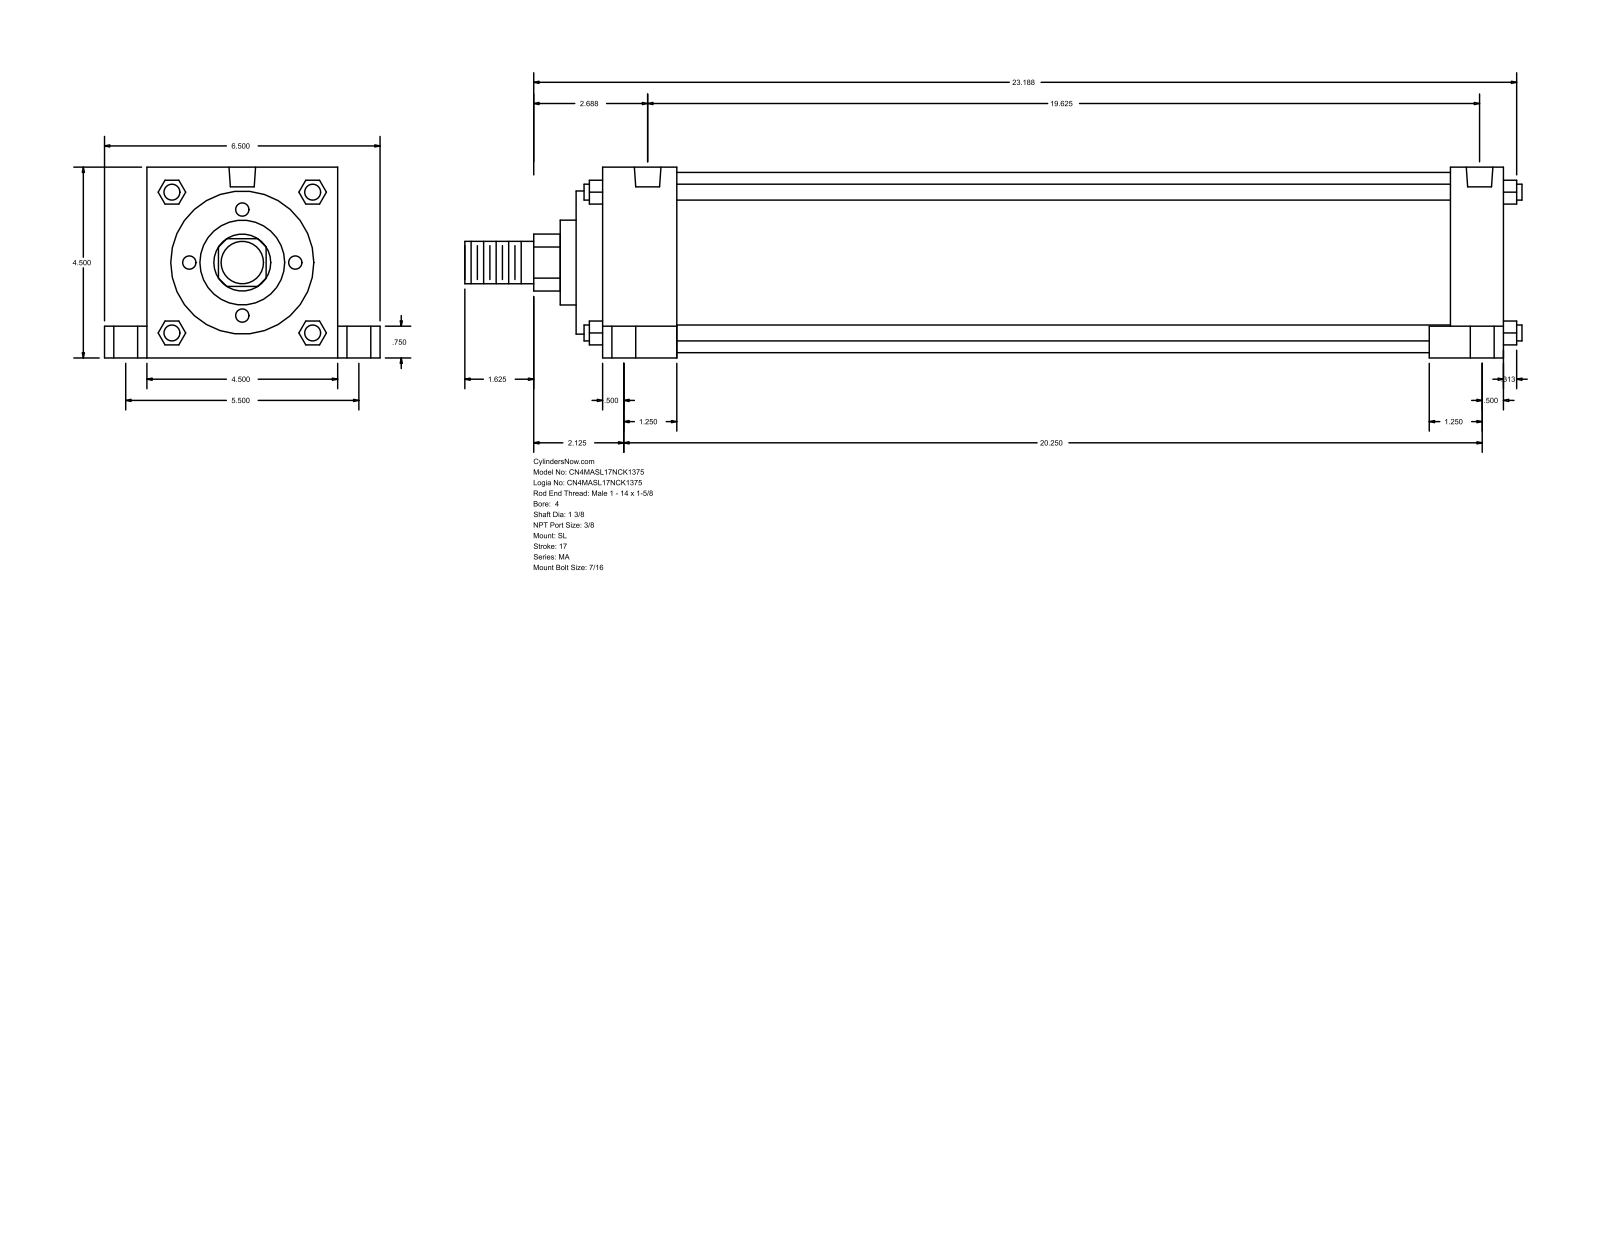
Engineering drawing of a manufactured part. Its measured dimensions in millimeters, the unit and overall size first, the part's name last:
Units: millimetres
Overall size (bounding box): 633.41 × 165.1 × 114.3
Round holes (diameter × count): ⌀11.11 ×4, ⌀14.29 ×4, ⌀20.64 ×4, ⌀15.93 ×2
Round bosses / shafts (diameter × count): ⌀9.53 ×4, ⌀107.95 ×1, ⌀85.72 ×1, ⌀50.8 ×1, ⌀34.92 ×1, ⌀25.4 ×1
Partial cylindrical surfaces — rounded edges, fillets, slot ends (radius × count): R17.06 ×1
Main face-to-face distances: 114.3, 539.75, 463.55, 555.62, 15.87, 60.32, 44.45, 495.3, 523.87, 508
Hole centre spacings: 69.87, 70.14, 71.29, 72.4, 139.7, 488.95, 500.2, 504.92
Bodies: 0 solids, 150 faces (113 planar, 37 cylindrical, 0 other)
Part name (STEP PRODUCT): MA_SL__0400_1.375
STEP written by: GSSL Pune (CONFIG_CONTROL_DESIGN)
